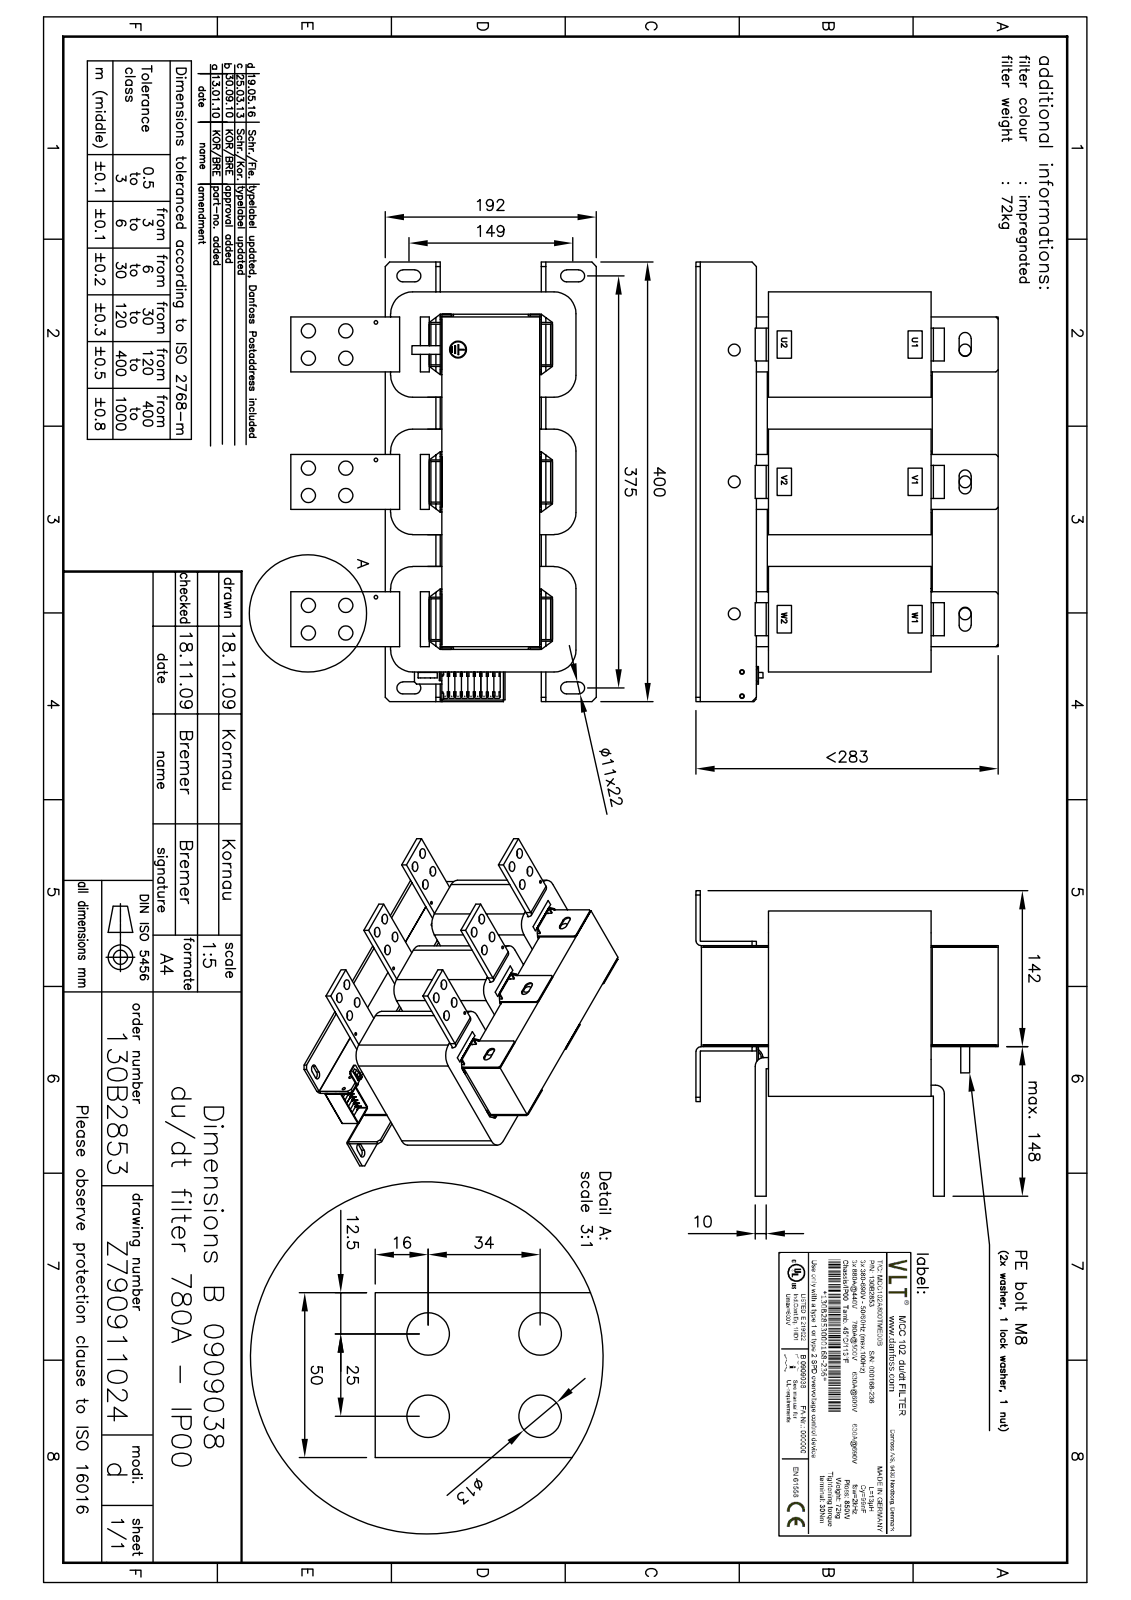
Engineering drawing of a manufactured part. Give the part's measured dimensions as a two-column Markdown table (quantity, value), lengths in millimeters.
| quantity | value |
| --- | --- |
| part name | Luftspalt 1 für B 0909038; #700-1266; curved spring lock washer_din_Spring washer DIN 128 - A8; 130B2853 (+8 more) |
| STEP written by | SolidWorks 2014 (AUTOMOTIVE_DESIGN) |
| units | millimeters |
| bodies | 103 solids, 1847 faces (1307 planar, 262 cylindrical, 278 other) |
| overall size | 400 × 281.8 × 275.5 |
| volume | 13 760 000 mm³ |
| surface area | 1 827 000 mm² |
| round holes (diameter × count) | 13 × 12, 3.3 × 6, 6.8 × 6, 8 × 6, 8.4 × 6, 15 × 6, 4.1 × 5, 4.3 × 5, 8.2 × 5, 4.5 × 4, 11 × 3, 4 × 2 |
| round bosses / shafts (diameter × count) | 16 × 6, 14 × 5, 9.9 × 5, 9 × 5, 8 × 5, 7.6 × 5, 24 × 3, 4 × 3 |
| partial cylindrical surfaces (radius × count) | 5.5 × 22, 0.1 × 19, 1.6 × 17, 30 × 12, 5.25 × 3, 1 × 2, 4 × 2, 5 × 2 |
| main face-to-face distances | 1.5, 31.5, 125, 90, 30, 88.5, 63, 250, 61.5, 0.4 |
| hole center spacings | 125, 129.54, 25, 28.5, 34, 42.2, 42.57, 61.96 |
